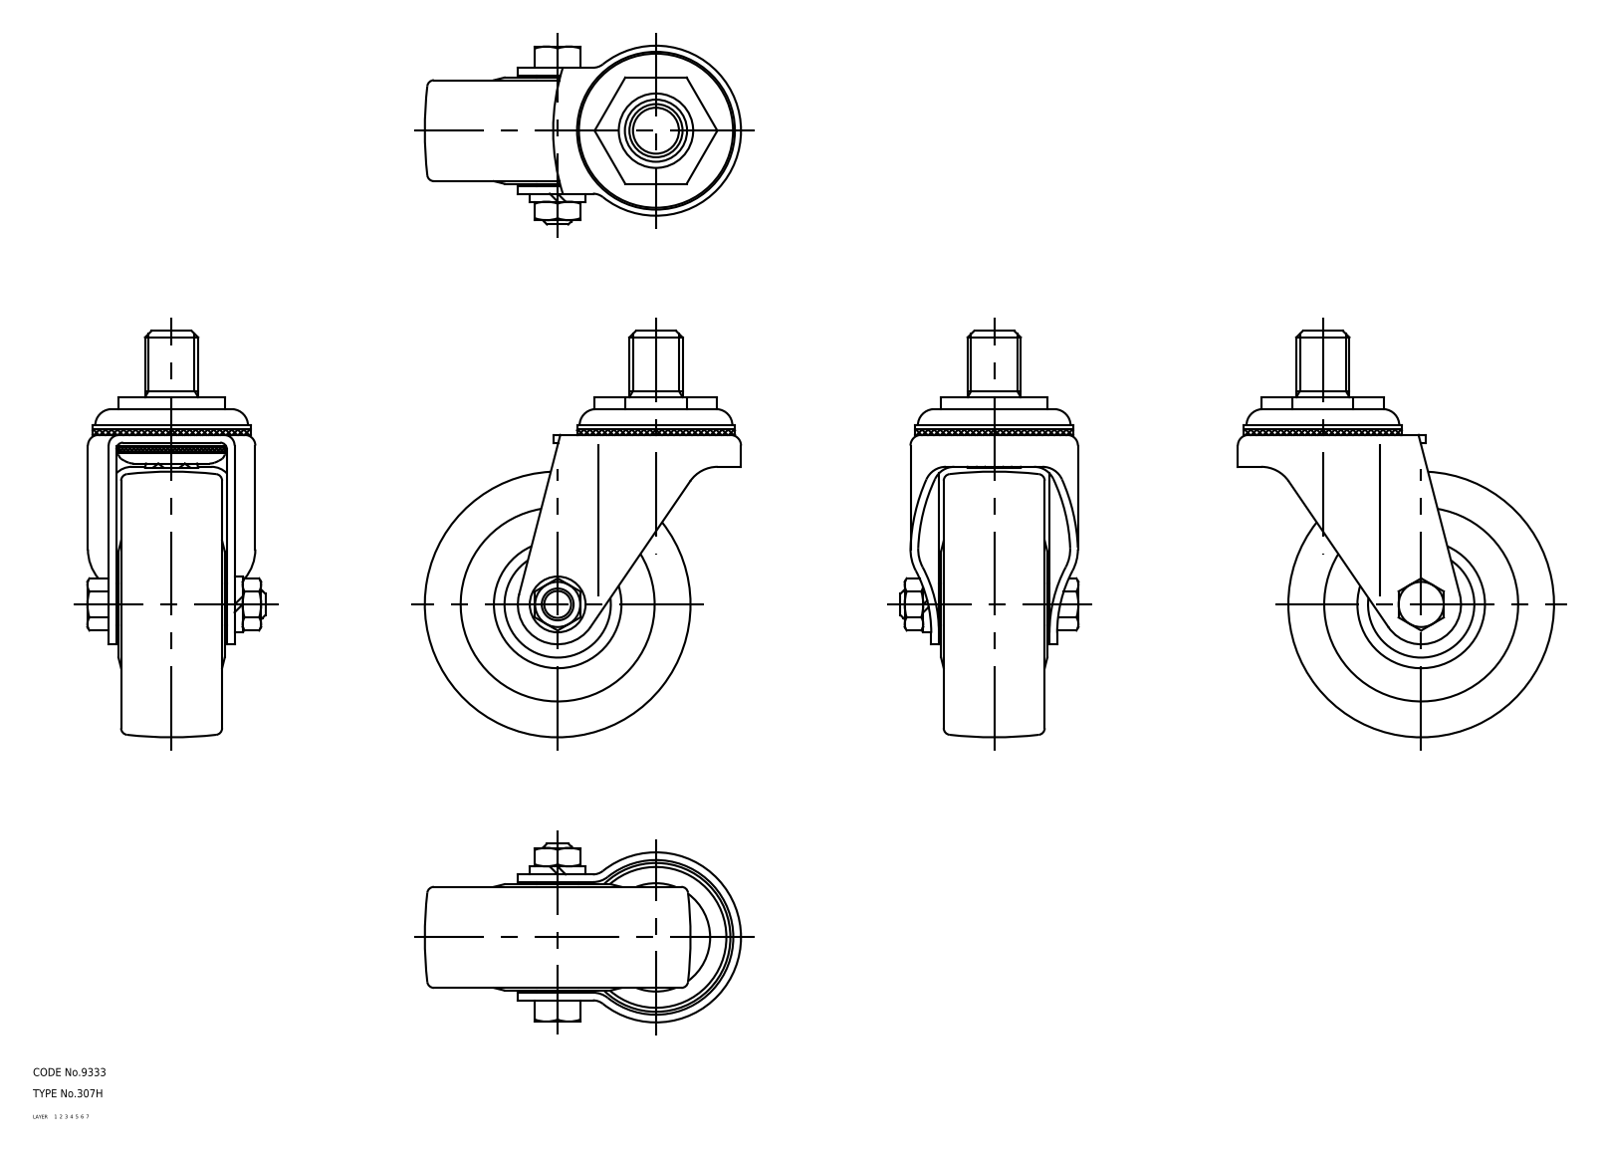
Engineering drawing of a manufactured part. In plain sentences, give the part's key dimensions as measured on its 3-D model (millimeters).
The part is named "67123266; 67123279; 67123292; 67123305". Its 3-D file was written by "CADfix (AUTOMOTIVE_DESIGN)". It is 4 solids with 214 faces: 0 planar, 0 cylindrical and 214 other. Overall it measures 153 by 119 by 67 millimeters. Its volume is 333 915 cubic millimeters and its surface area 70 189 square millimeters.
